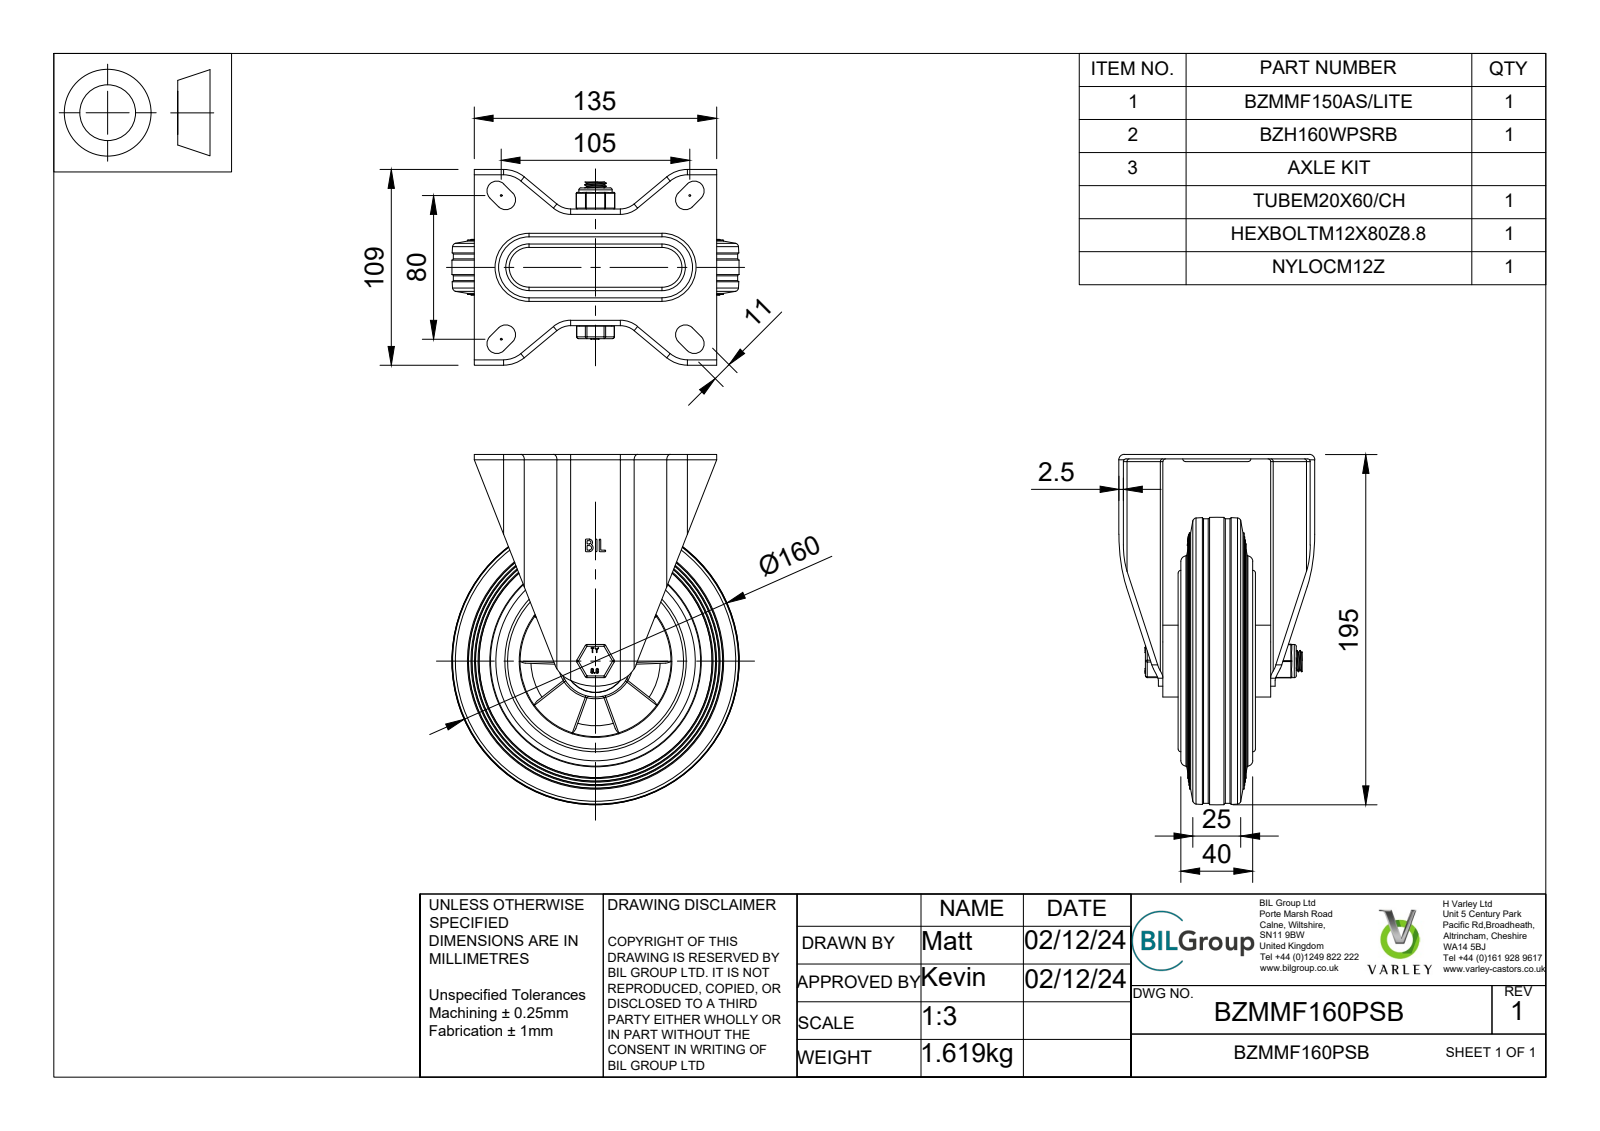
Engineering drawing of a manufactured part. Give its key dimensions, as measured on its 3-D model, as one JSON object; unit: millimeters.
{"part_name": "BZMMF160PSB v3; BZMMF150ASLITE v1; ZINC PLATED, PRESSED STEEL BRACKET; BZH160WPSRB v1 (+7 more)", "step_written_by": "Autodesk Translation Framework v13.20.0.188 (AP242_MANAGED_MODEL_BASED_3D_ENGINEERING_MIM_LF)", "units": "millimeters", "bodies": {"solids": 17, "faces": 745, "planar": 224, "cylindrical": 191, "other": 330}, "overall_size": [195, 160, 109], "volume_mm3": 694881, "surface_area_mm2": 224596, "round_holes": [[12, 1], [12.25, 1], [12.5, 1], [14, 1], [20, 1], [34, 1], [35, 1], [72, 1], [85, 1], [94, 1]], "round_bosses_or_shafts": [[7.5, 8], [158.4, 1], [101, 1], [40, 1], [34.9, 1], [19.9, 1], [18.5, 1], [18, 1]], "partial_cylinders_radius": [[0.5, 18], [1, 12], [1.5, 12], [3, 8], [5.5, 8], [2, 4], [6, 4], [9, 4]], "face_to_face_distances": [2.5, 24.24, 60, 62.5, 21.74, 1, 35.25, 26.74, 18.75, 46.25]}
